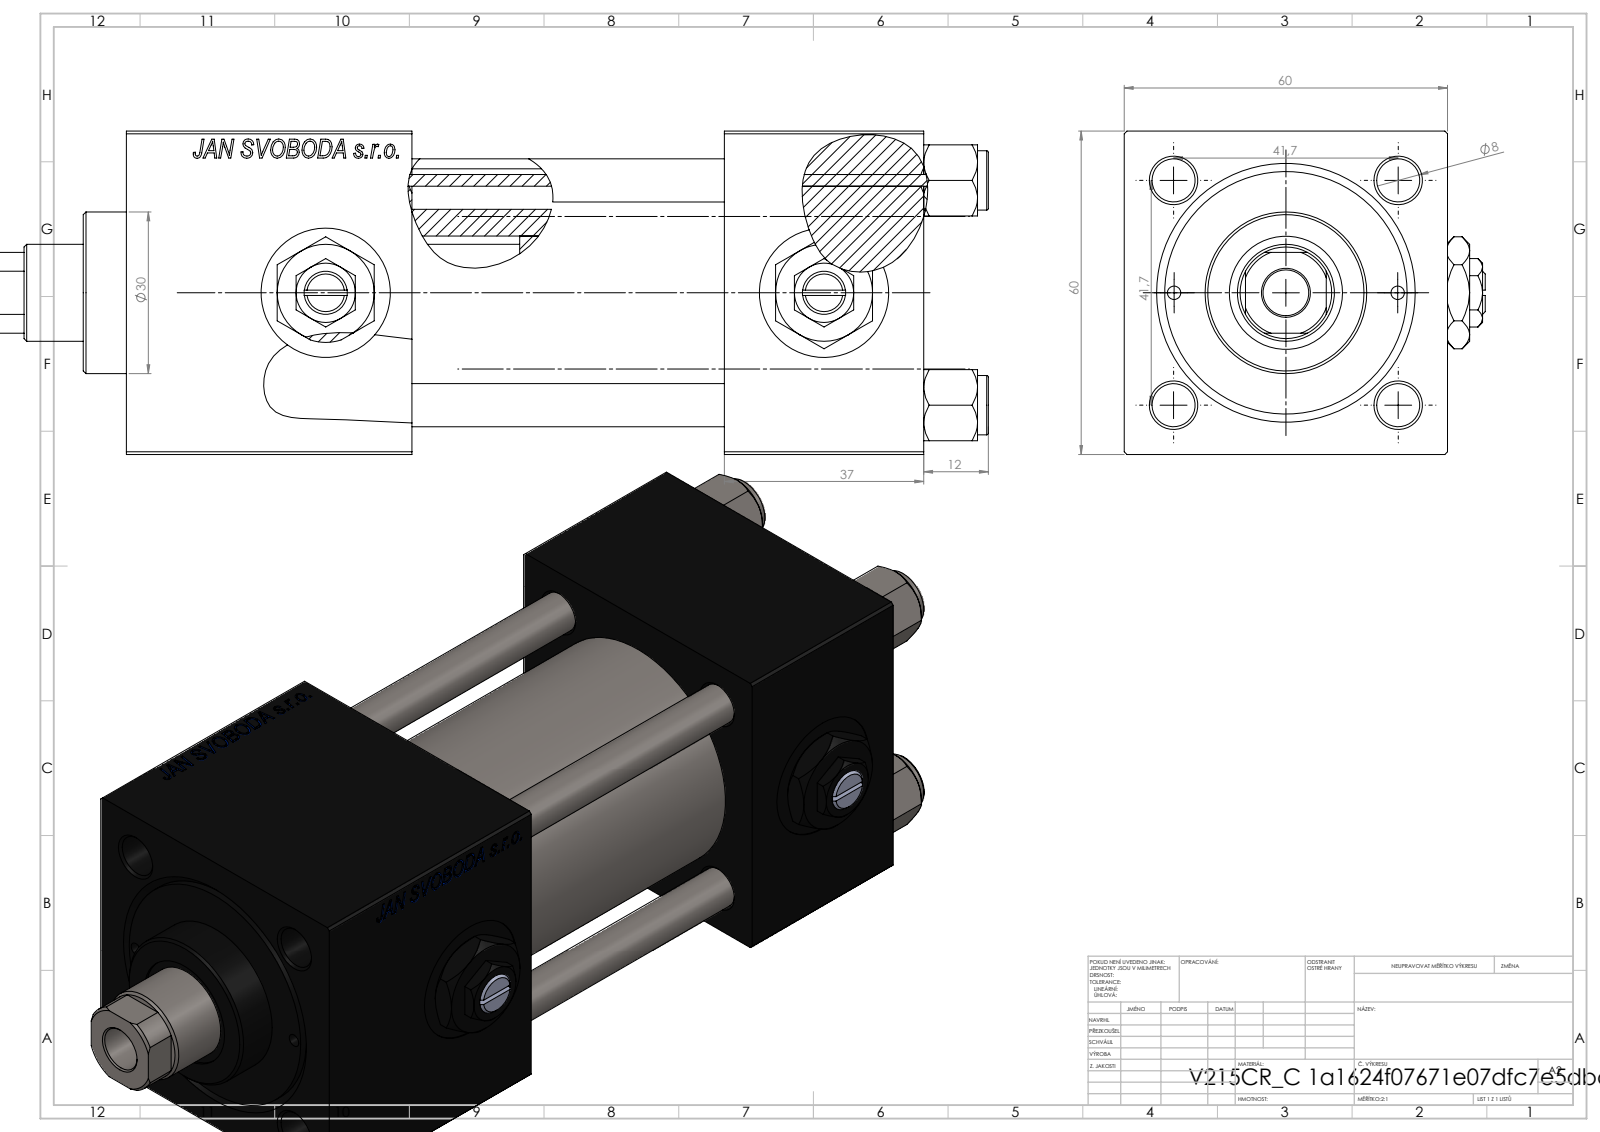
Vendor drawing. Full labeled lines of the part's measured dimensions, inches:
Part name (STEP PRODUCT): NUT_M5_C; Zatka_pro_OIL_PORT; V215CR_C_Body; V215CR_C_TYCINKA (+2 more)
STEP written by: SolidWorks 2019 (CONFIG_CONTROL_DESIGN)
Units: inches
Bodies: 13 solids, 1256 faces (576 planar, 102 cylindrical, 578 other)
Overall size (bounding box): 7.283 × 2.638 × 2.362
Volume: 24.37 in³ · Surface area: 167.9 in²
Round holes (diameter × count): ⌀0.315 ×4, ⌀0.098 ×2, ⌀0.276 ×2, ⌀0.656 ×2, ⌀0.945 ×2, ⌀0.335 ×1, ⌀0.709 ×1, ⌀0.827 ×1, ⌀1.22 ×1, ⌀1.575 ×1, ⌀1.772 ×1
Round bosses / shafts (diameter × count): ⌀0.433 ×4, ⌀1.811 ×1, ⌀1.181 ×1
Partial cylindrical surfaces — rounded edges, fillets, slot ends (radius × count): R0.335 ×1
Main face-to-face distances: 2.362, 1.457, 2.087, 5.827, 4.37, 2.283, 3.74, 4.697, 3.24, 0.957
Hole centre spacings: 0.821, 1.161, 1.642, 1.832, 0.817, 2.322, 1.634, 3.642
